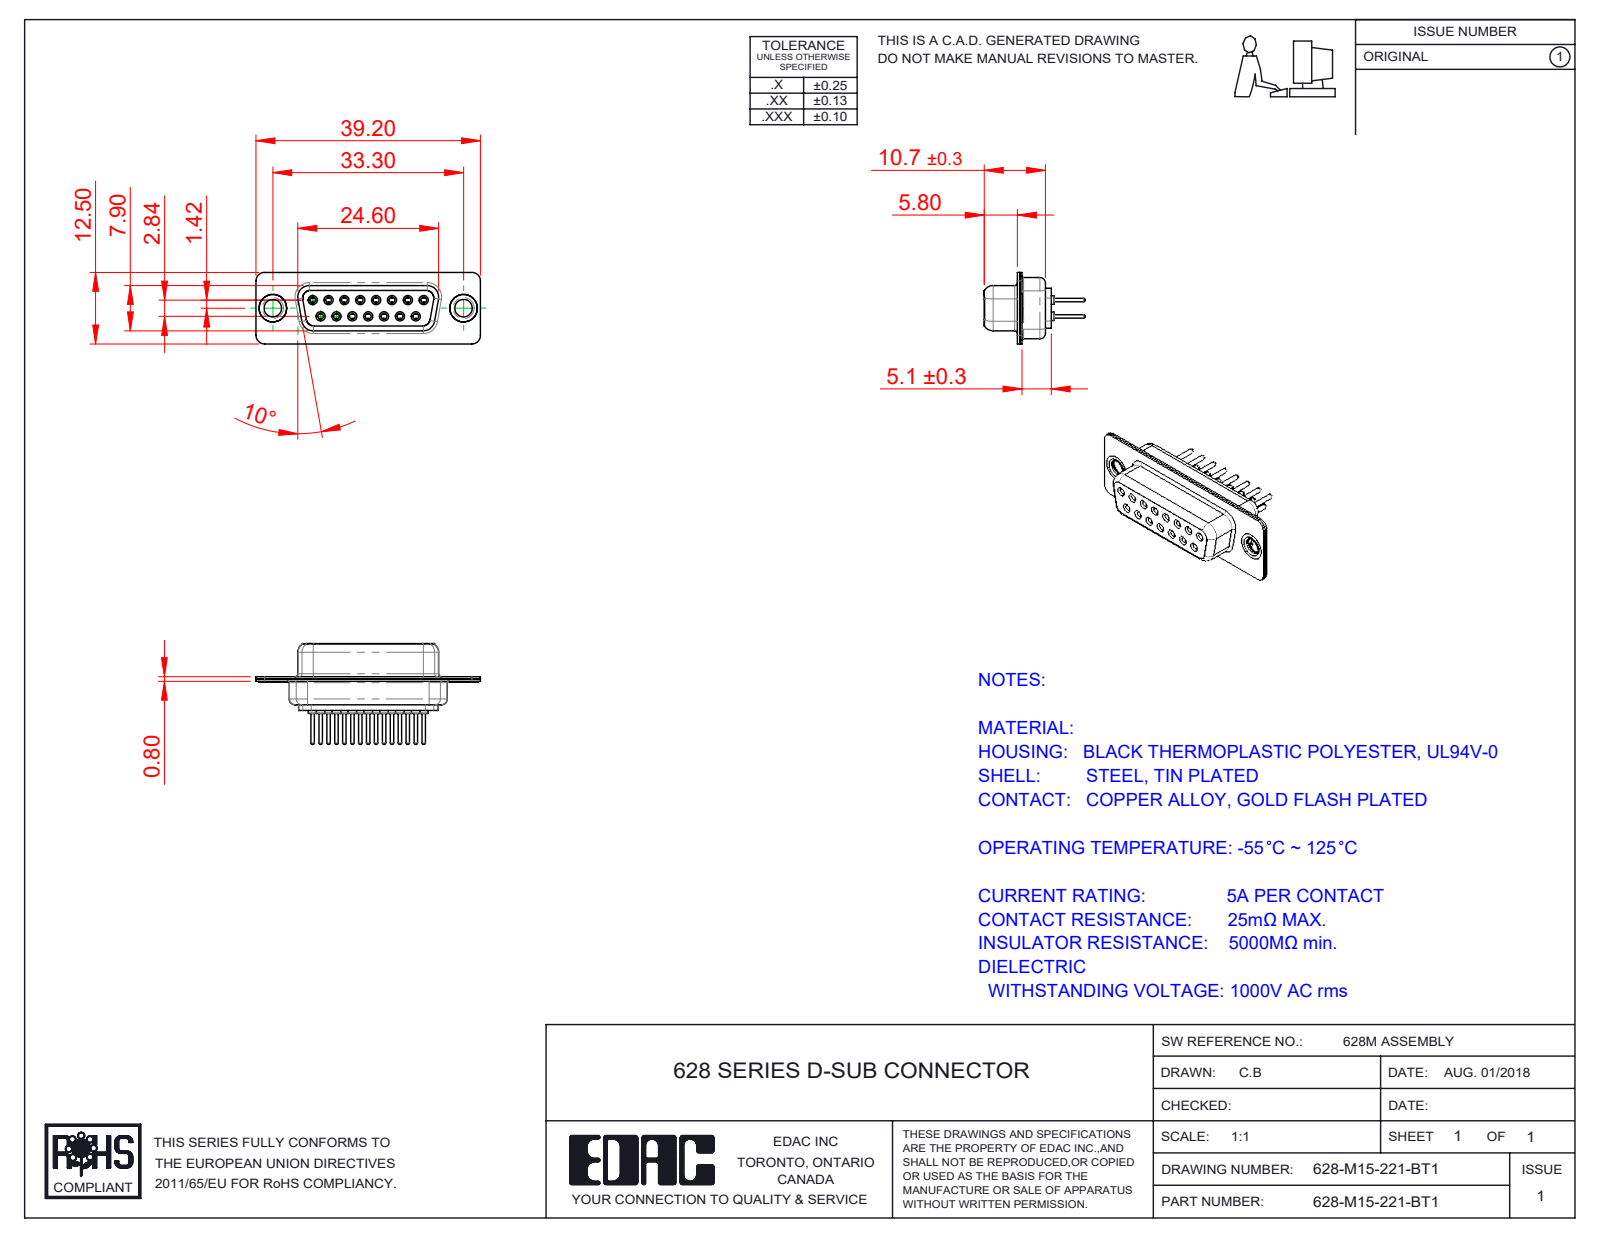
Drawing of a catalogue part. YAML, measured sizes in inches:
part_name: "628M Shell Rear_15 Contacts; 628M Contact Row 2_21; 628M Contact Row 1_21; 628M Shell Front_15 Contacts (+3 more)"
step_written_by: "SolidWorks 2020 (CONFIG_CONTROL_DESIGN)"
units: inches
bodies: {solids: 20, faces: 1078, planar: 292, cylindrical: 406, other: 380}
overall_size: [1.543, 0.693, 0.492]
volume: 0.146
surface_area: 9.384
round_holes:
  - {diameter: 0.039, count: 15}
  - {diameter: 0.043, count: 15}
  - {diameter: 0.067, count: 15}
  - {diameter: 0.071, count: 15}
  - {diameter: 0.079, count: 15}
  - {diameter: 0.12, count: 2}
  - {diameter: 0.157, count: 2}
  - {diameter: 0.189, count: 2}
round_bosses_or_shafts:
  - {diameter: 0.087, count: 15}
  - {diameter: 0.063, count: 15}
  - {diameter: 0.059, count: 15}
  - {diameter: 0.024, count: 15}
  - {diameter: 0.197, count: 2}
  - {diameter: 0.193, count: 2}
  - {diameter: 0.14, count: 2}
partial_cylinders:
  - {radius: 0.059, count: 16}
  - {radius: 0.079, count: 12}
  - {radius: 0.053, count: 8}
  - {radius: 0.063, count: 8}
  - {radius: 0.01, count: 4}
  - {radius: 0.02, count: 4}
  - {radius: 0.024, count: 4}
  - {radius: 0.026, count: 4}
face_to_face_distances: [0.016, 0.055, 0.018, 0.333, 0.35, 0.071, 0.244, 0.278, 0.039, 0.053]
hole_center_spacings: [0.124, 0.109, 0.218, 0.327, 0.436, 0.198, 0.198, 0.294]
